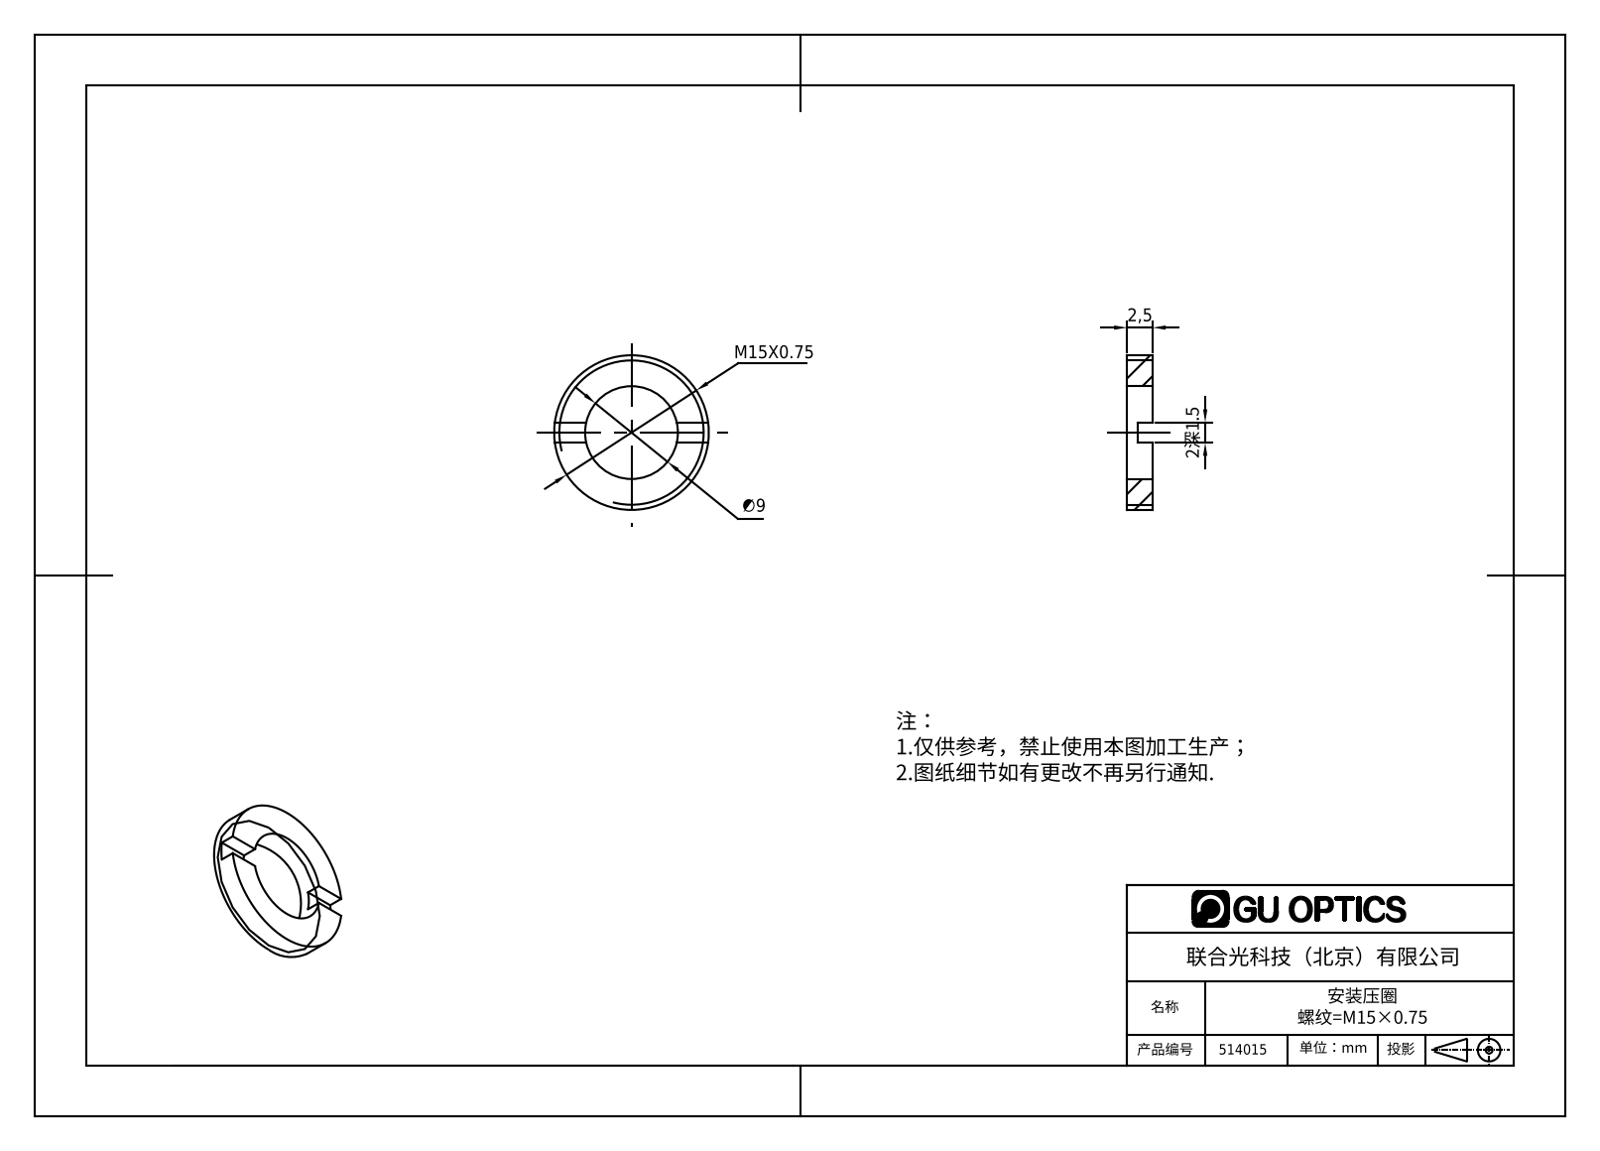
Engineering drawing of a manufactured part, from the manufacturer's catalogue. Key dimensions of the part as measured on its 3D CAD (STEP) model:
Part name (STEP PRODUCT): 514015
STEP written by: SolidWorks 2016 (CONFIG_CONTROL_DESIGN)
Units: millimetres
Bodies: 1 solid, 13 faces (9 planar, 4 cylindrical, 0 other)
Overall size (bounding box): 15 × 15 × 2.5
Volume: 265 mm³ · Surface area: 421 mm²
Round holes (diameter × count): ⌀9 ×1
Round bosses / shafts (diameter × count): ⌀15 ×1
Main face-to-face distances: 2.5, 1, 1.5, 2
